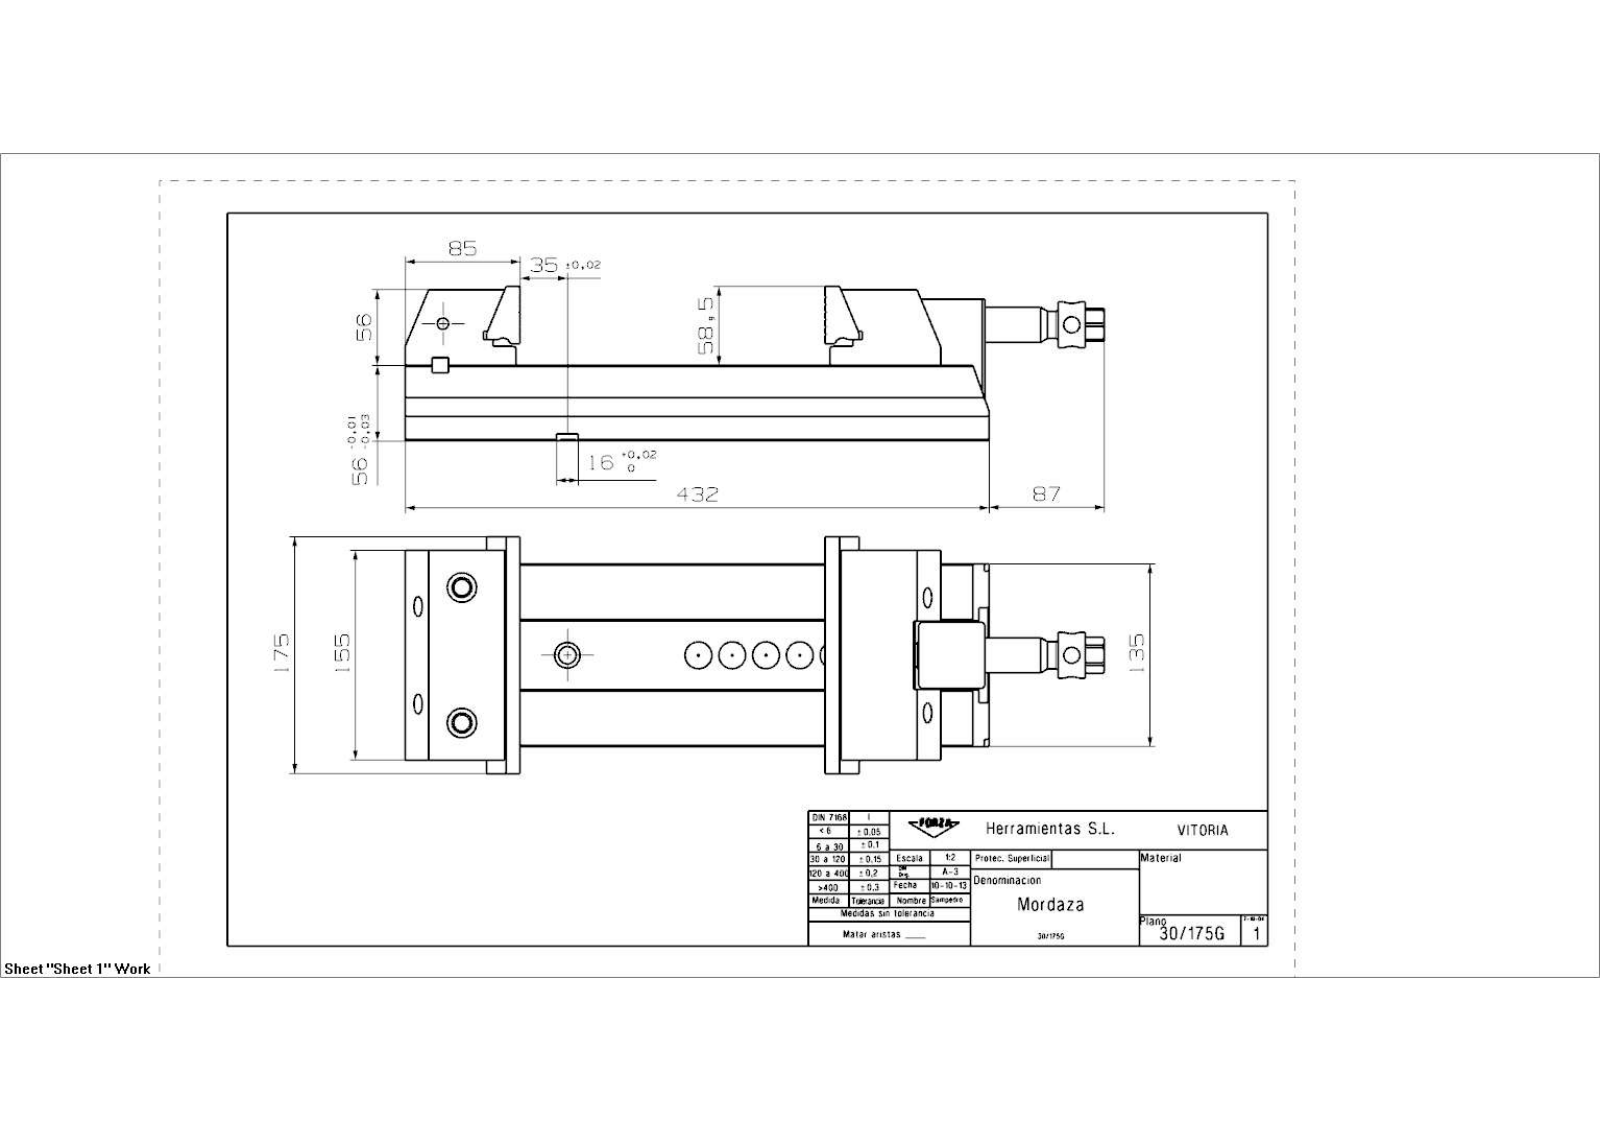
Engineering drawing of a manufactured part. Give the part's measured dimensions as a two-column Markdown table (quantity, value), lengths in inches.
| quantity | value |
| --- | --- |
| part name | 30_175G_Mordaza |
| STEP written by | SIEMENS PLM Software NX 7.5 (CONFIG_CONTROL_DESIGN) |
| units | inches |
| bodies | 12 solids, 469 faces (313 planar, 95 cylindrical, 61 other) |
| overall size | 20.363 × 6.89 × 4.508 |
| volume | 232.6 in³ |
| surface area | 760 in² |
| round holes (diameter × count) | 0.512 × 6, 0.591 × 6, 0.748 × 6, 0.204 × 5, 0.275 × 4, 0.335 × 4, 0.417 × 4, 0.346 × 3, 0.374 × 2, 0.394 × 2, 0.472 × 2, 0.487 × 2 |
| round bosses / shafts (diameter × count) | 1.339 × 1, 1.331 × 1, 1.024 × 1, 0.787 × 1, 0.65 × 1 |
| partial cylindrical surfaces (radius × count) | 0.315 × 4, 0.787 × 4, 0.063 × 2, 0.236 × 2, 0.276 × 2, 0.157 × 1, 0.354 × 1, 0.413 × 1 |
| main face-to-face distances | 2.205, 0.953, 1.252, 5.315, 0.394, 4.411, 3.459, 2.207, 1.28, 4.035 |
| hole center spacings | 0.256, 3.091, 2.835, 3.346, 4.176, 1.093, 1.094, 1.144 |
